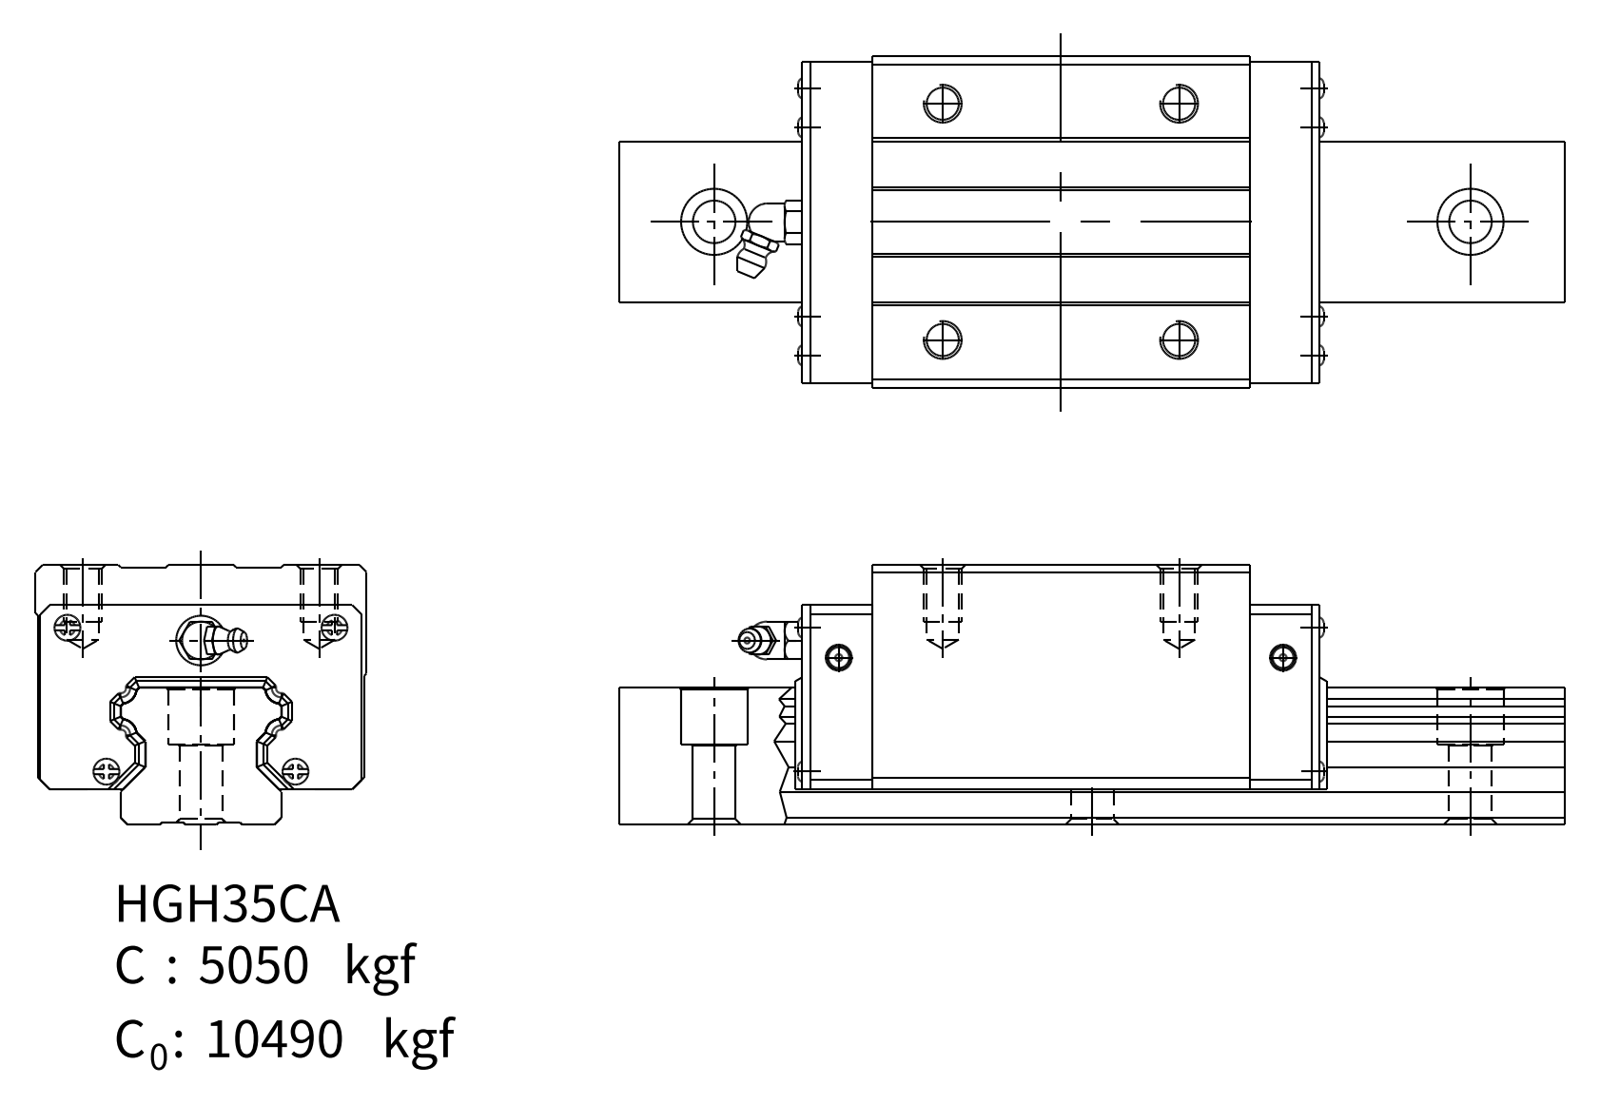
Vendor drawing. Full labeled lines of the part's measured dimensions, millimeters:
Part name (STEP PRODUCT): HGH35CA
STEP written by: SolidWorks 2006104 (CONFIG_CONTROL_DESIGN)
Units: millimetres
Bodies: 1 solid, 373 faces (297 planar, 16 cylindrical, 60 other)
Overall size (bounding box): 112.7 × 70 × 47.5
Volume: 278 307 mm³ · Surface area: 37 362 mm²
Round holes (diameter × count): ⌀8 ×4
Partial cylindrical surfaces — rounded edges, fillets, slot ends (radius × count): R1.2 ×4, R3.25 ×4
Main face-to-face distances: 0.5, 47.5, 21.5, 26, 69.5, 112.4, 69, 39.05, 17.55, 8.45
Hole centre spacings: 50, 70.71
